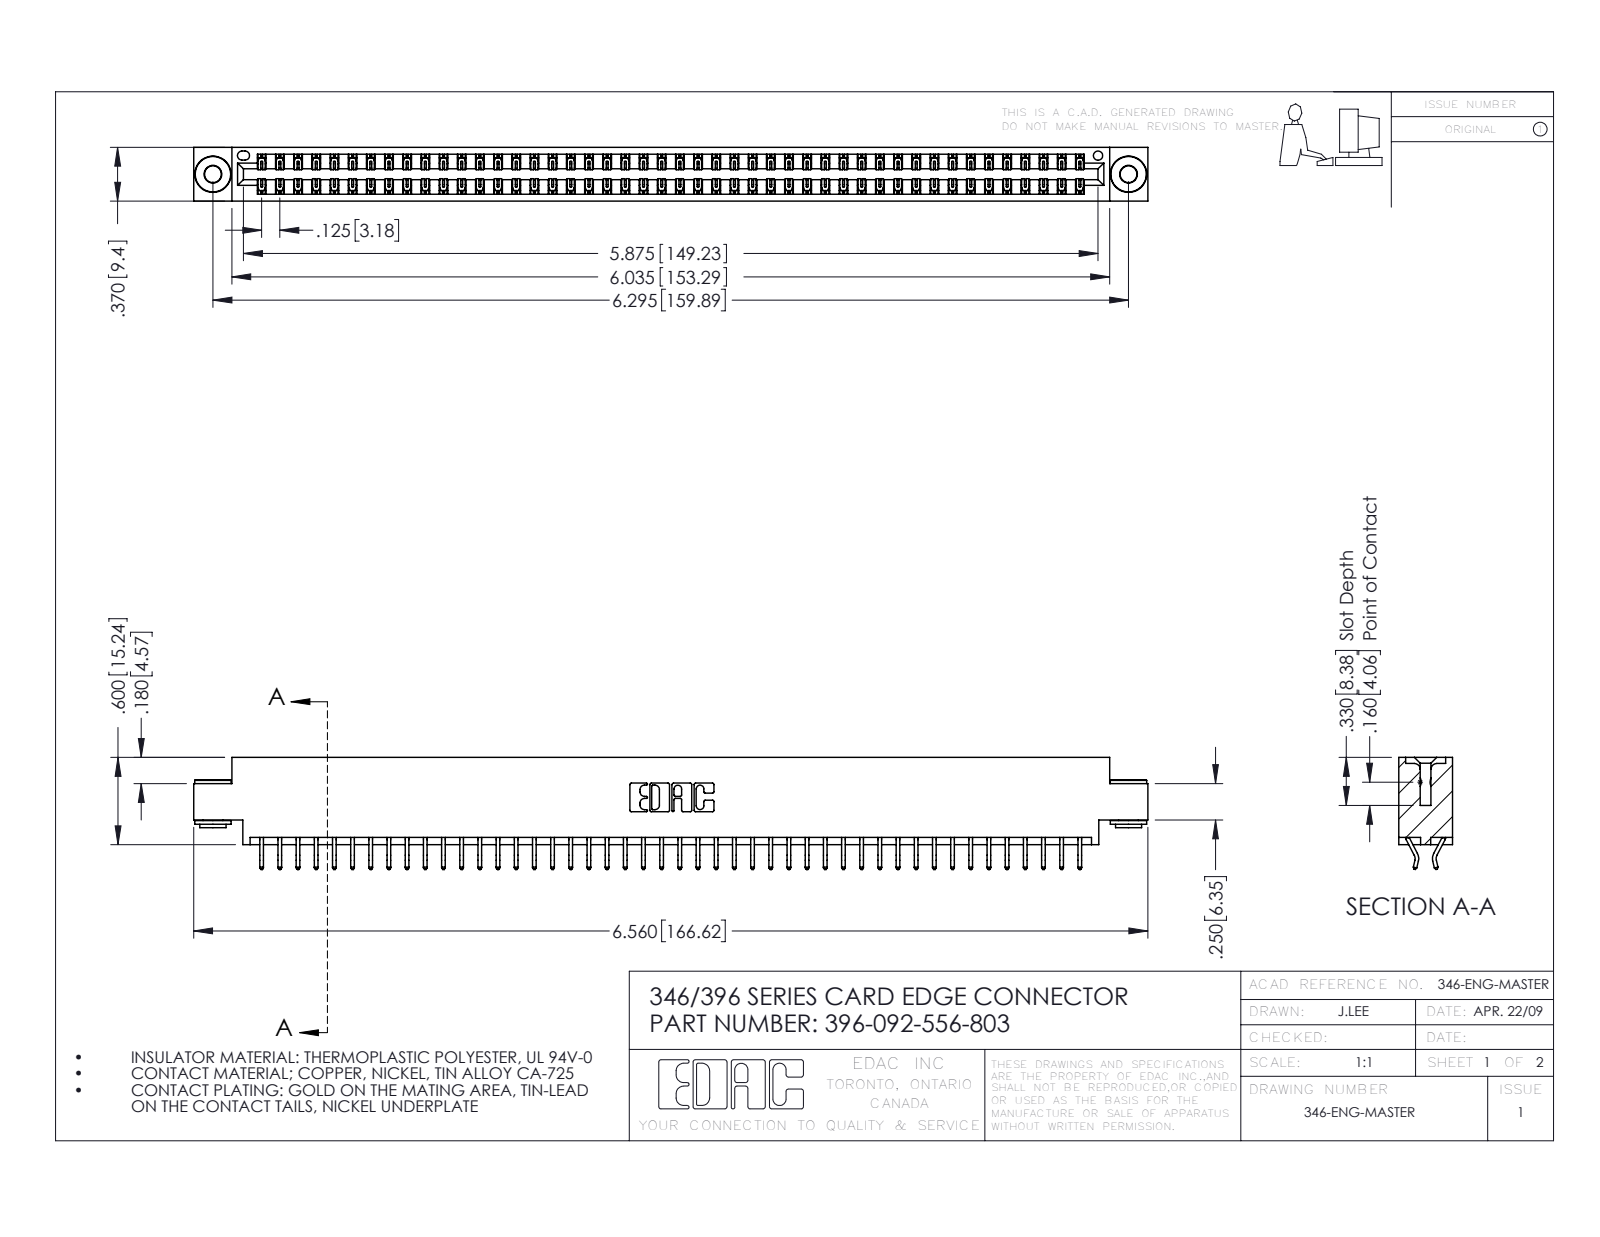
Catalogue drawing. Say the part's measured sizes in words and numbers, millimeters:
The part is named "345-292-001_556 Tail; 345-250-002_345-250-002-102; 396-092-556-803; 346 Part_0.170 Offset - 0.156 Dia-TH". Its 3-D file was written by "SolidWorks 2016 (CONFIG_CONTROL_DESIGN)". It is 95 solids with 5500 faces: 3678 planar, 1814 cylindrical and 8 other. Overall it measures 166.6 by 19.6 by 9.4 millimeters. Its volume is 16 100 cubic millimeters and its surface area 22 550 square millimeters. Round holes: 2 of diameter 2.9, 2 of diameter 4, 1 of diameter 1.6. Round bosses or shafts: 2 of diameter 6.4, 2 of diameter 4.6, 2 of diameter 3.5. Partial cylindrical surfaces (rounded edges, fillets, slot ends): 138 of radius 0.2, 22 of radius 0.3, 6 of radius 0.2, 6 of radius 0.8, 3 of radius 0.7, 2 of radius 0.3, 2 of radius 0.4, 2 of radius 0.6. The main face-to-face distances are 1.2, 8.2, 9.4, 6.4, 0.6, 7, 1.8, 7.6, 3.8, 5.6. The hole center spacings are 6.2, 154.6, 159.9.
